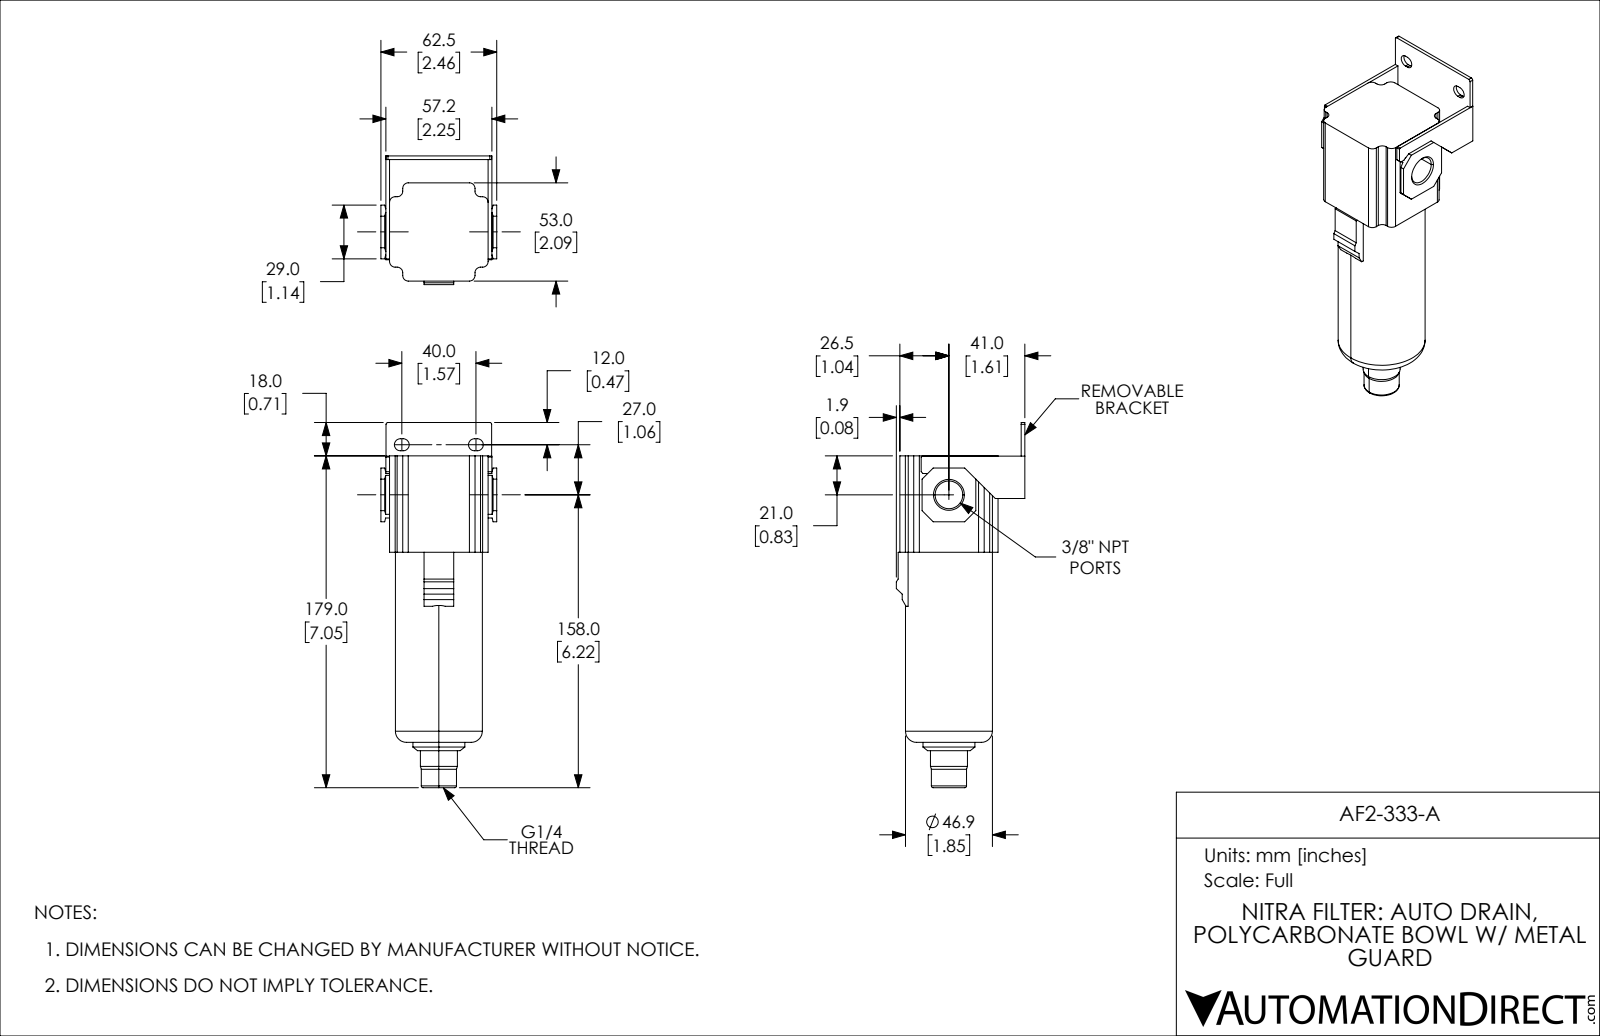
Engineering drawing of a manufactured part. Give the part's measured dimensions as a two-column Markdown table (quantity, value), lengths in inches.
| quantity | value |
| --- | --- |
| part name | AF2-333-A |
| STEP written by | SolidWorks 2019 (CONFIG_CONTROL_DESIGN) |
| units | inches |
| bodies | 1 solid, 137 faces (91 planar, 32 cylindrical, 14 other) |
| overall size | 7.756 × 2.733 × 2.461 |
| volume | 20.09 in³ |
| surface area | 65.35 in² |
| round holes (diameter × count) | 0.337 × 1, 0.589 × 1 |
| round bosses / shafts (diameter × count) | 1.846 × 1, 1.102 × 1, 0.787 × 1, 0.748 × 1 |
| partial cylindrical surfaces (radius × count) | 0.118 × 12, 0.128 × 4, 0.039 × 2 |
| main face-to-face distances | 0.079, 0.492, 0.571, 2.657, 2.579, 2.087, 2.173, 2.094, 0.104, 0.183 |
